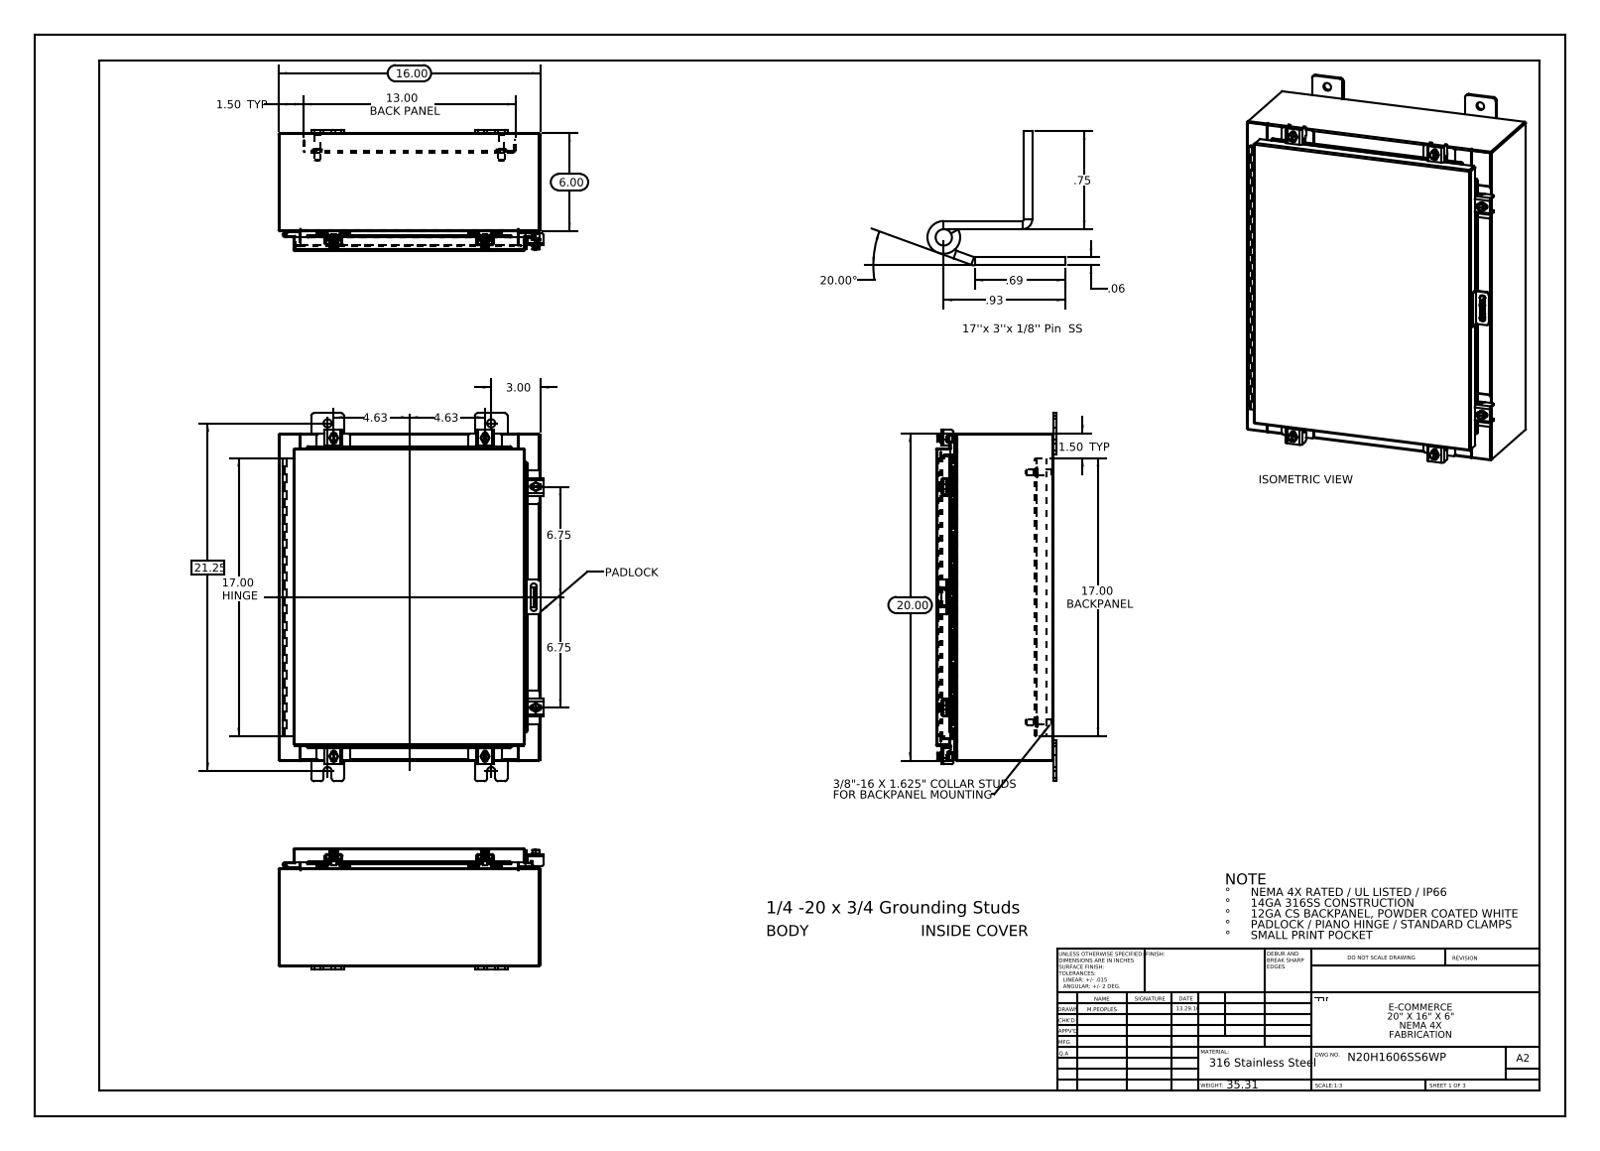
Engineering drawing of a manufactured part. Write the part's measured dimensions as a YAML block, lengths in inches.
part_name: "N20H1606SS6WP Mounting Feet; N20H1606SS6WP Hinge Enclosure Side2; N20H1606SS6WP Clamp Top; N20H1606SS6WP Mounting Studs (+8 more)"
step_written_by: "SolidWorks 2013 (CONFIG_CONTROL_DESIGN)"
units: inches
bodies: {solids: 49, faces: 1639, planar: 866, cylindrical: 665, other: 108}
overall_size: [22.5, 16.211, 7.389]
volume: 125
surface_area: 3150
round_holes:
  - {diameter: 0.5, count: 8}
  - {diameter: 0.213, count: 6}
  - {diameter: 0.26, count: 6}
  - {diameter: 0.125, count: 2}
  - {diameter: 0.125, count: 1}
round_bosses_or_shafts:
  - {diameter: 0.25, count: 7}
  - {diameter: 0.5, count: 6}
  - {diameter: 0.399, count: 6}
  - {diameter: 0.625, count: 4}
  - {diameter: 0.375, count: 4}
  - {diameter: 0.33, count: 4}
  - {diameter: 0.315, count: 2}
  - {diameter: 0.236, count: 2}
partial_cylinders:
  - {radius: 0.06, count: 30}
  - {radius: 0.013, count: 25}
  - {radius: 0.19, count: 24}
  - {radius: 0.088, count: 21}
  - {radius: 0.12, count: 12}
  - {radius: 0.141, count: 12}
  - {radius: 0.125, count: 10}
  - {radius: 0.05, count: 9}
face_to_face_distances: [0.075, 7.126, 7.051, 7.201, 0.104, 15.925, 1, 1.075, 6.051, 6.126]
hole_center_spacings: [17.38, 1.858, 2.276, 2.326, 2.326, 3.065, 4.297, 9.25]
